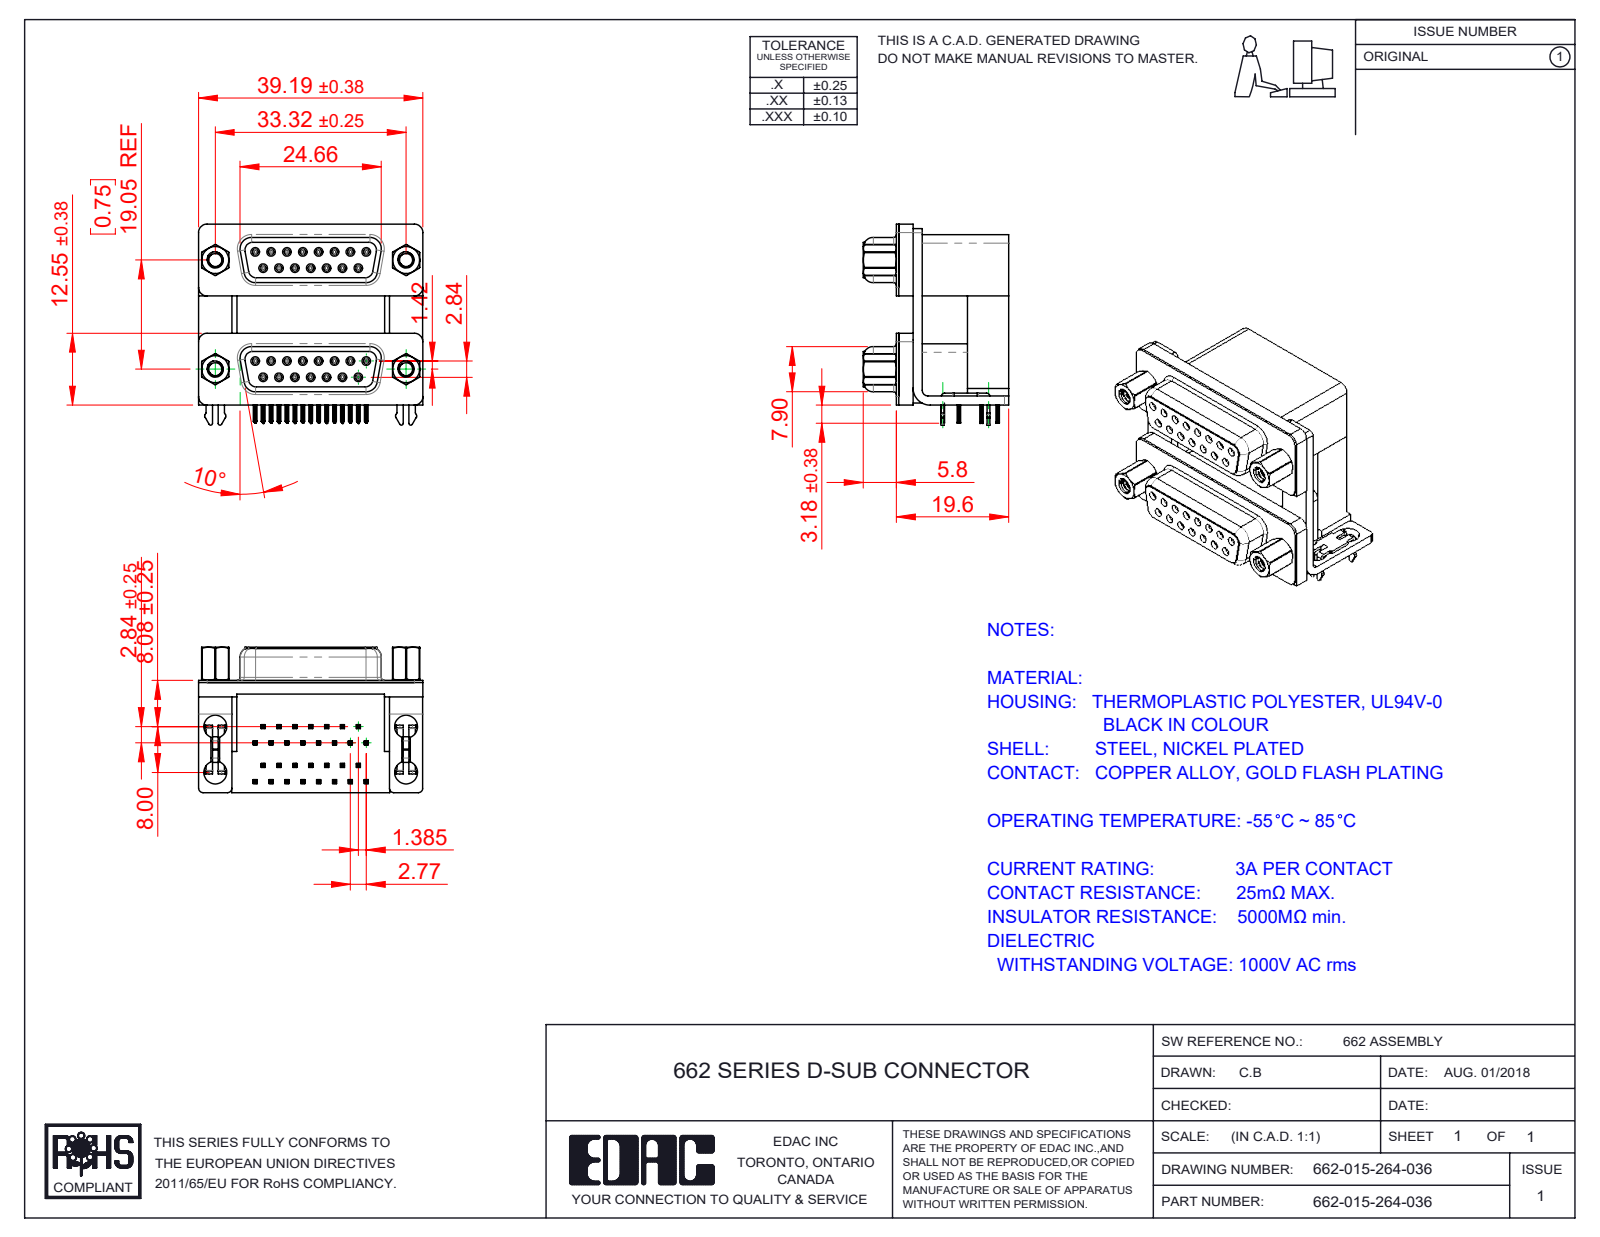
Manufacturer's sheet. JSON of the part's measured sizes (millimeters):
{"part_name": "662 Housing Upper_15 Contacts M; 662 2 Prong Board Lock_3; 662 Shell_15 Contacts; 662 Contact Bottom Upper_M (+8 more)", "step_written_by": "SolidWorks 2020 (CONFIG_CONTROL_DESIGN)", "units": "millimeters", "bodies": {"solids": 47, "faces": 5266, "planar": 2342, "cylindrical": 1368, "other": 1556}, "overall_size": [39.19, 35.1, 25.4], "volume_mm3": 16447, "surface_area_mm2": 19146, "round_holes": [[0.8, 30], [0.9, 30], [4, 8], [2.26, 4], [2.29, 4], [3.5, 4], [4.8, 4], [5, 4]], "round_bosses_or_shafts": [[1.2, 30], [4.9, 4], [4.75, 4], [3.9, 4], [2.79, 4]], "partial_cylinders_radius": [[0.1, 242], [0.15, 120], [0.35, 60], [0.34, 30], [1.35, 16], [1.5, 16], [0.28, 14], [0.5, 12]], "face_to_face_distances": [0.4, 19.05, 19.2, 12, 2.5, 16.7, 2.9, 7.2, 9.5, 12.4], "hole_center_spacings": [3.16, 19.25, 2.77, 19.84, 5.54, 8.31, 19.05, 20.78]}
